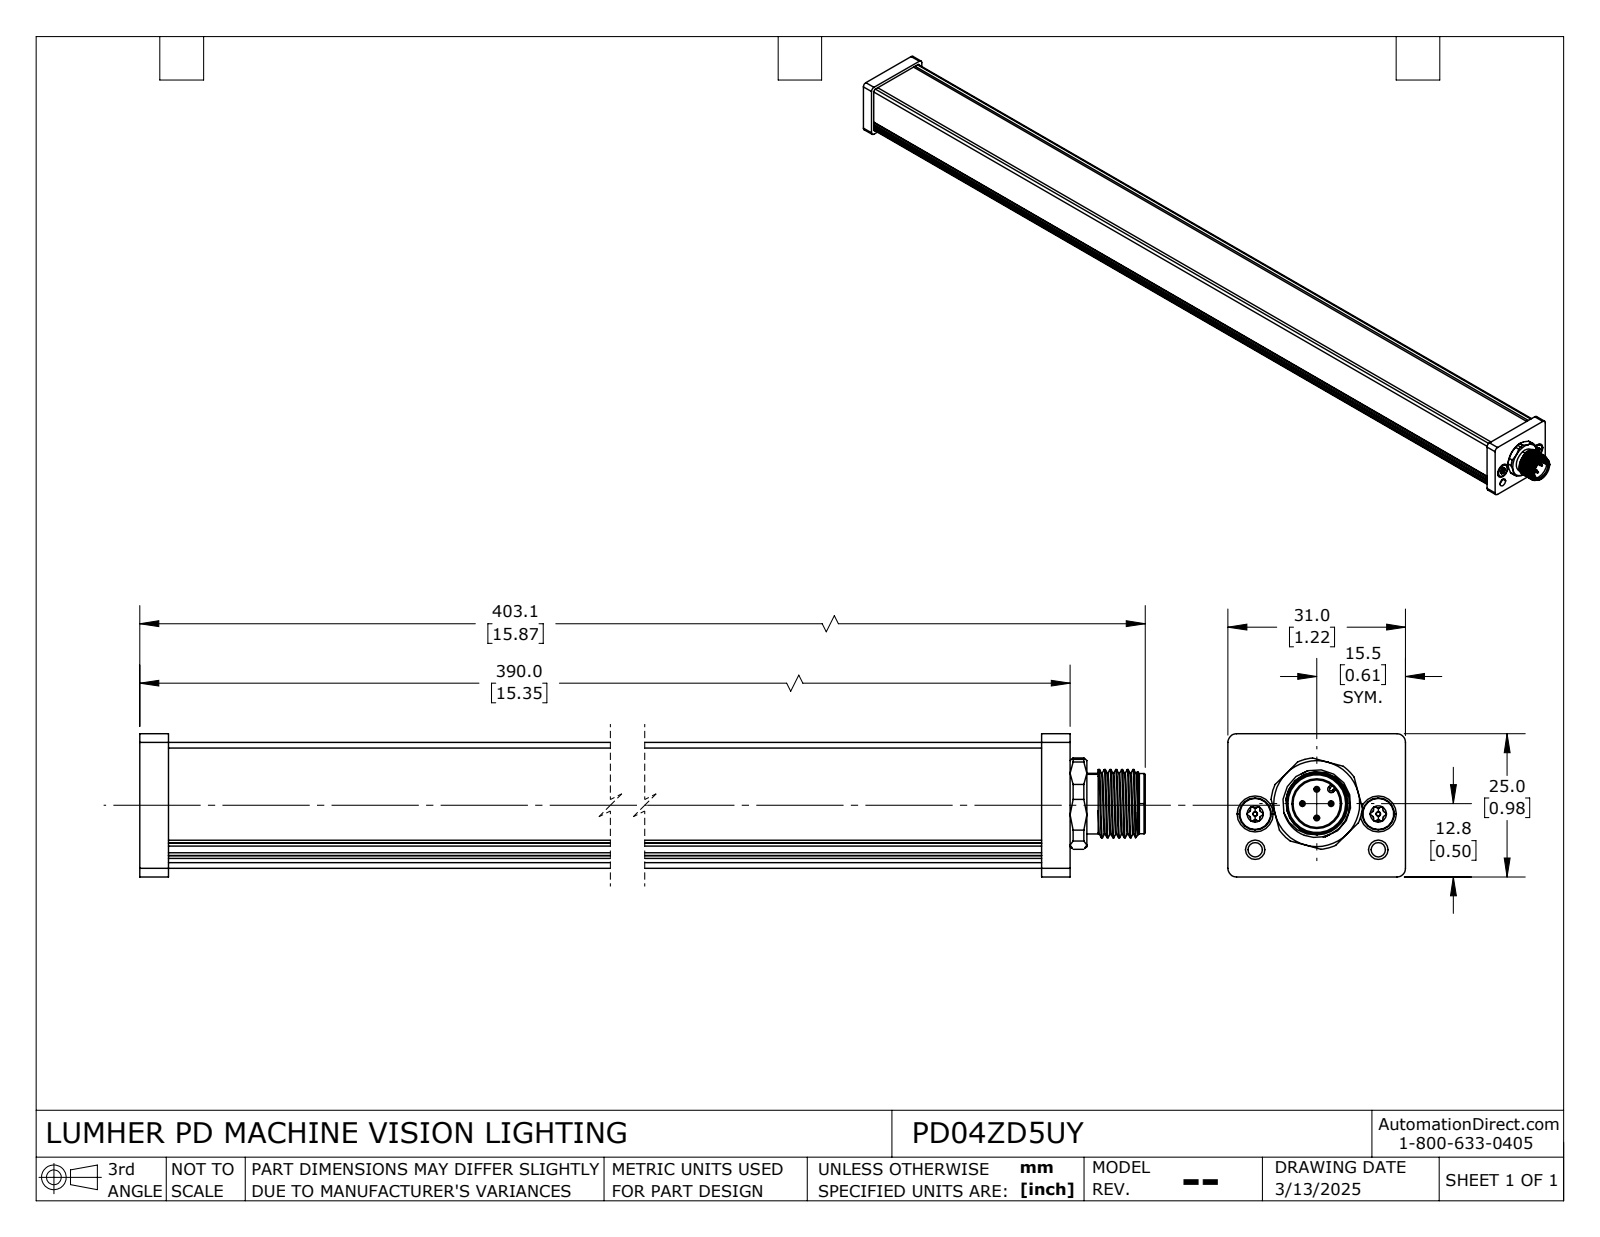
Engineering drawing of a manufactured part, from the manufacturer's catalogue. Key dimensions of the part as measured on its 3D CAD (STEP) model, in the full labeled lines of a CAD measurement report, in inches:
Part name (STEP PRODUCT): PD04__5_Y
STEP written by: SolidWorks 2024 (AUTOMOTIVE_DESIGN)
Units: inches
Bodies: 1 solid, 563 faces (89 planar, 296 cylindrical, 178 other)
Overall size (bounding box): 15.87 × 1.22 × 0.984
Volume: 14.09 in³ · Surface area: 82.88 in²
Round holes (diameter × count): ⌀0.057 ×4, ⌀0.134 ×4, ⌀0.098 ×2, ⌀0.327 ×1, ⌀0.37 ×1
Round bosses / shafts (diameter × count): ⌀0.055 ×4, ⌀0.039 ×4, ⌀0.22 ×2, ⌀0.118 ×2, ⌀0.031 ×2, ⌀0.469 ×1, ⌀0.417 ×1, ⌀0.413 ×1
Partial cylindrical surfaces — rounded edges, fillets, slot ends (radius × count): R0.022 ×24, R0.01 ×12, R0.02 ×8, R0.039 ×8, R0.118 ×6, R0.059 ×4, R0.012 ×2, R0.04 ×2
Main face-to-face distances: 1.102, 0.039, 0.059, 0.079, 0.118, 1.063, 0.866, 0.098, 0.856, 15.157
Hole centre spacings: 0.098, 0.139, 0.197, 0.246, 0.332, 0.424, 0.429, 0.454
